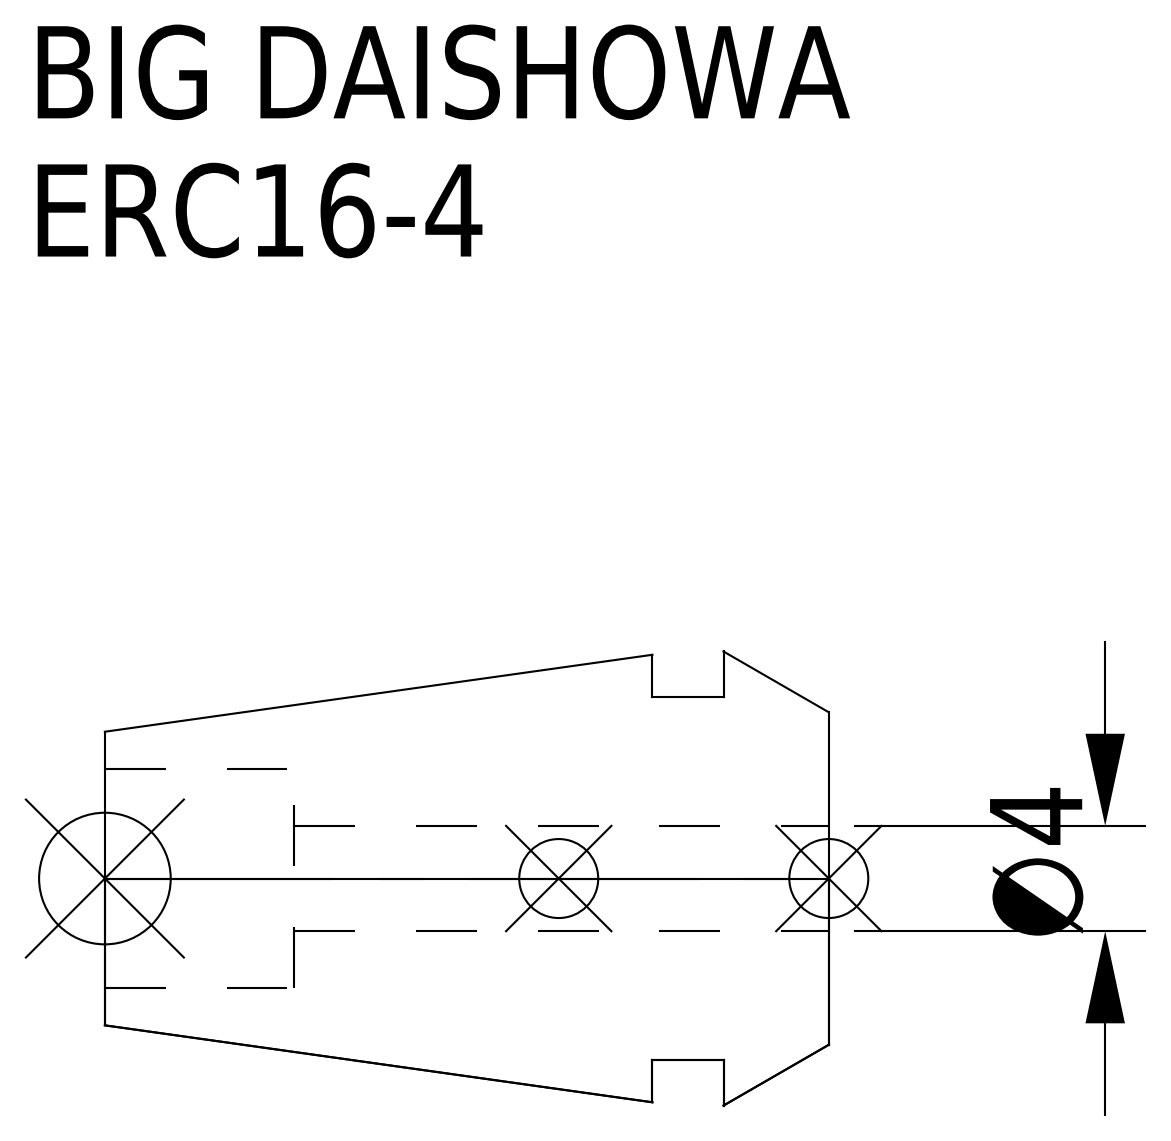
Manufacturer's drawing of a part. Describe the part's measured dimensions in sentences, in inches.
The part is named "ERC16-4". Its 3-D file was written by "CREO PARAMETRIC BY PTC INC, 2016380 (AUTOMOTIVE_DESIGN)". It is 1 solid with 15 faces: 5 planar, 6 cylindrical and 4 other. Overall it measures 1.083 by 0.679 by 0.679 inches. Its volume is 0.229 cubic inches and its surface area 3.201 square inches. Round holes: 1 of diameter 0.157, 1 of diameter 0.327. Round bosses or shafts: 1 of diameter 0.543. The main face-to-face distances are 0.157, 0.264, 0.106, 1.083, 0.925, 0.819, 0.799, 0.642, 0.535, 0.283.
